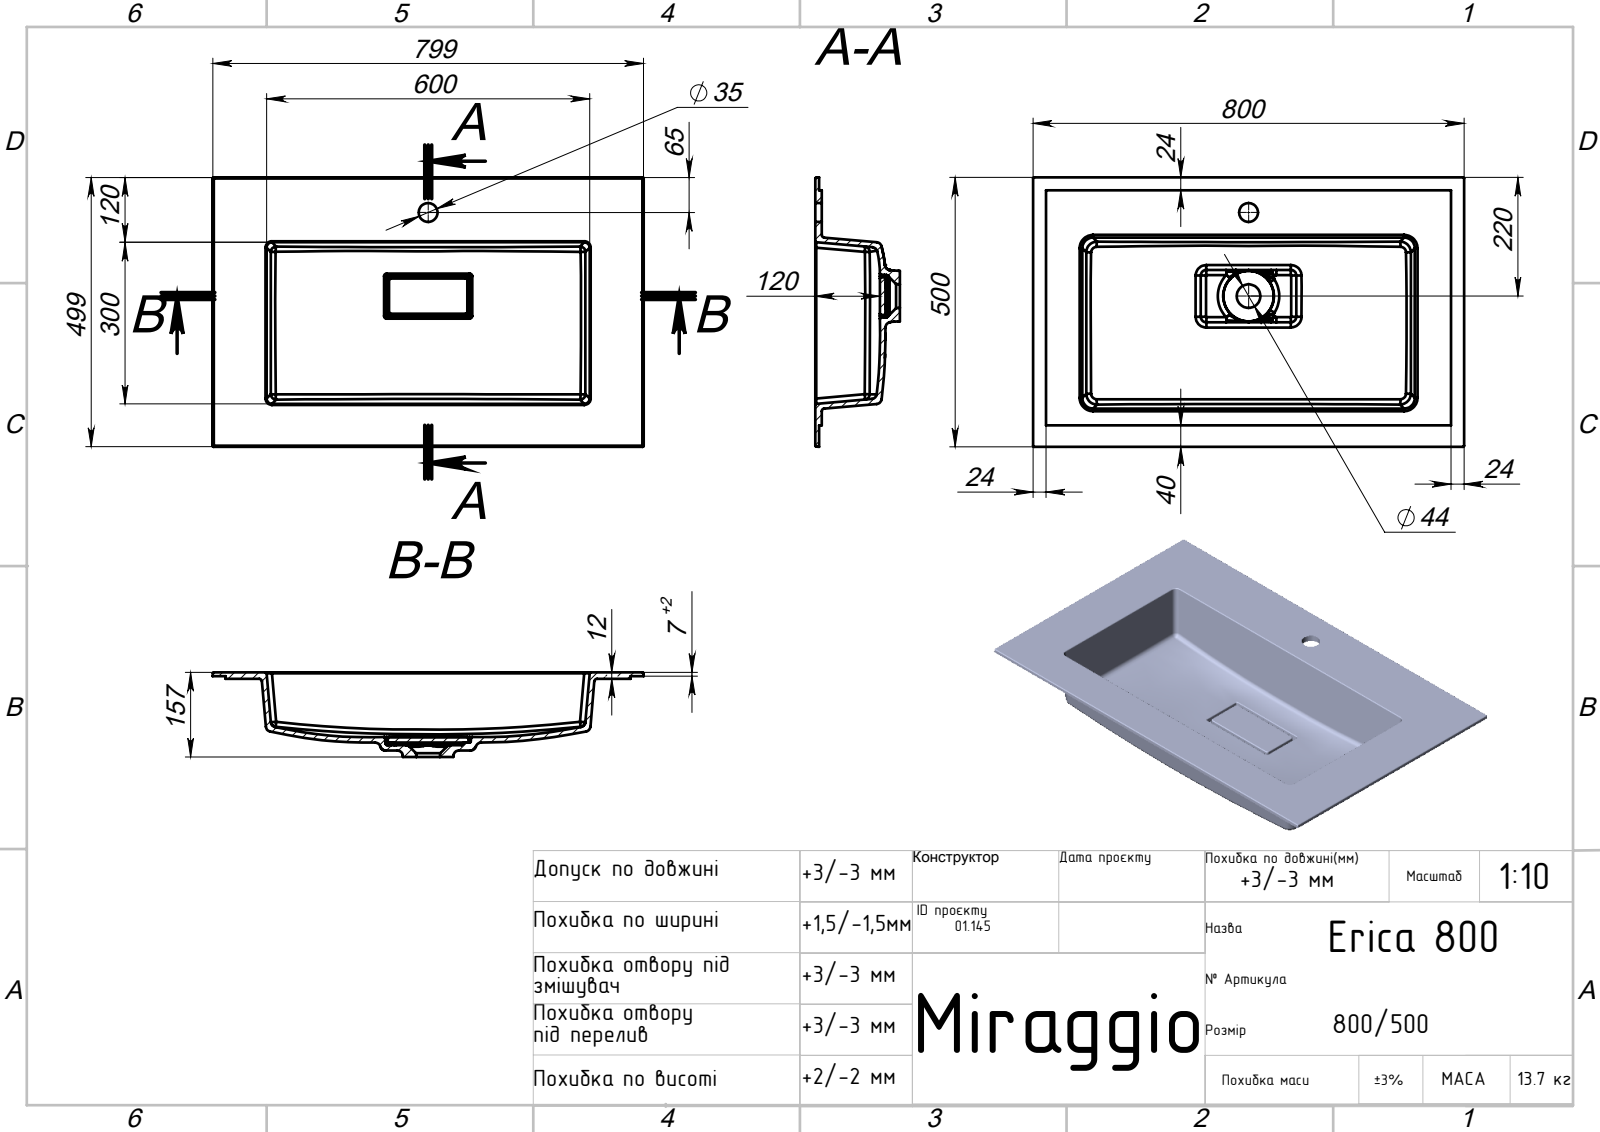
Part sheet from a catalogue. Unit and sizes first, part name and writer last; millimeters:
Units: millimetres
Overall size (bounding box): 800 × 500 × 157
Round holes (diameter × count): ⌀35 ×1
Partial cylindrical surfaces — rounded edges, fillets, slot ends (radius × count): R2 ×27, R3 ×19, R6 ×6, R5 ×4, R10 ×4, R20 ×4
Main face-to-face distances: 12, 10, 5, 7, 9.99, 123, 118, 130, 108, 113
Volume: 6 029 000 mm³ · Surface area: 1 190 000 mm²
Bodies: 2 solids, 244 faces (44 planar, 69 cylindrical, 131 other)
Part name (STEP PRODUCT): Erica 800
STEP written by: SolidWorks 2020 (AUTOMOTIVE_DESIGN)
